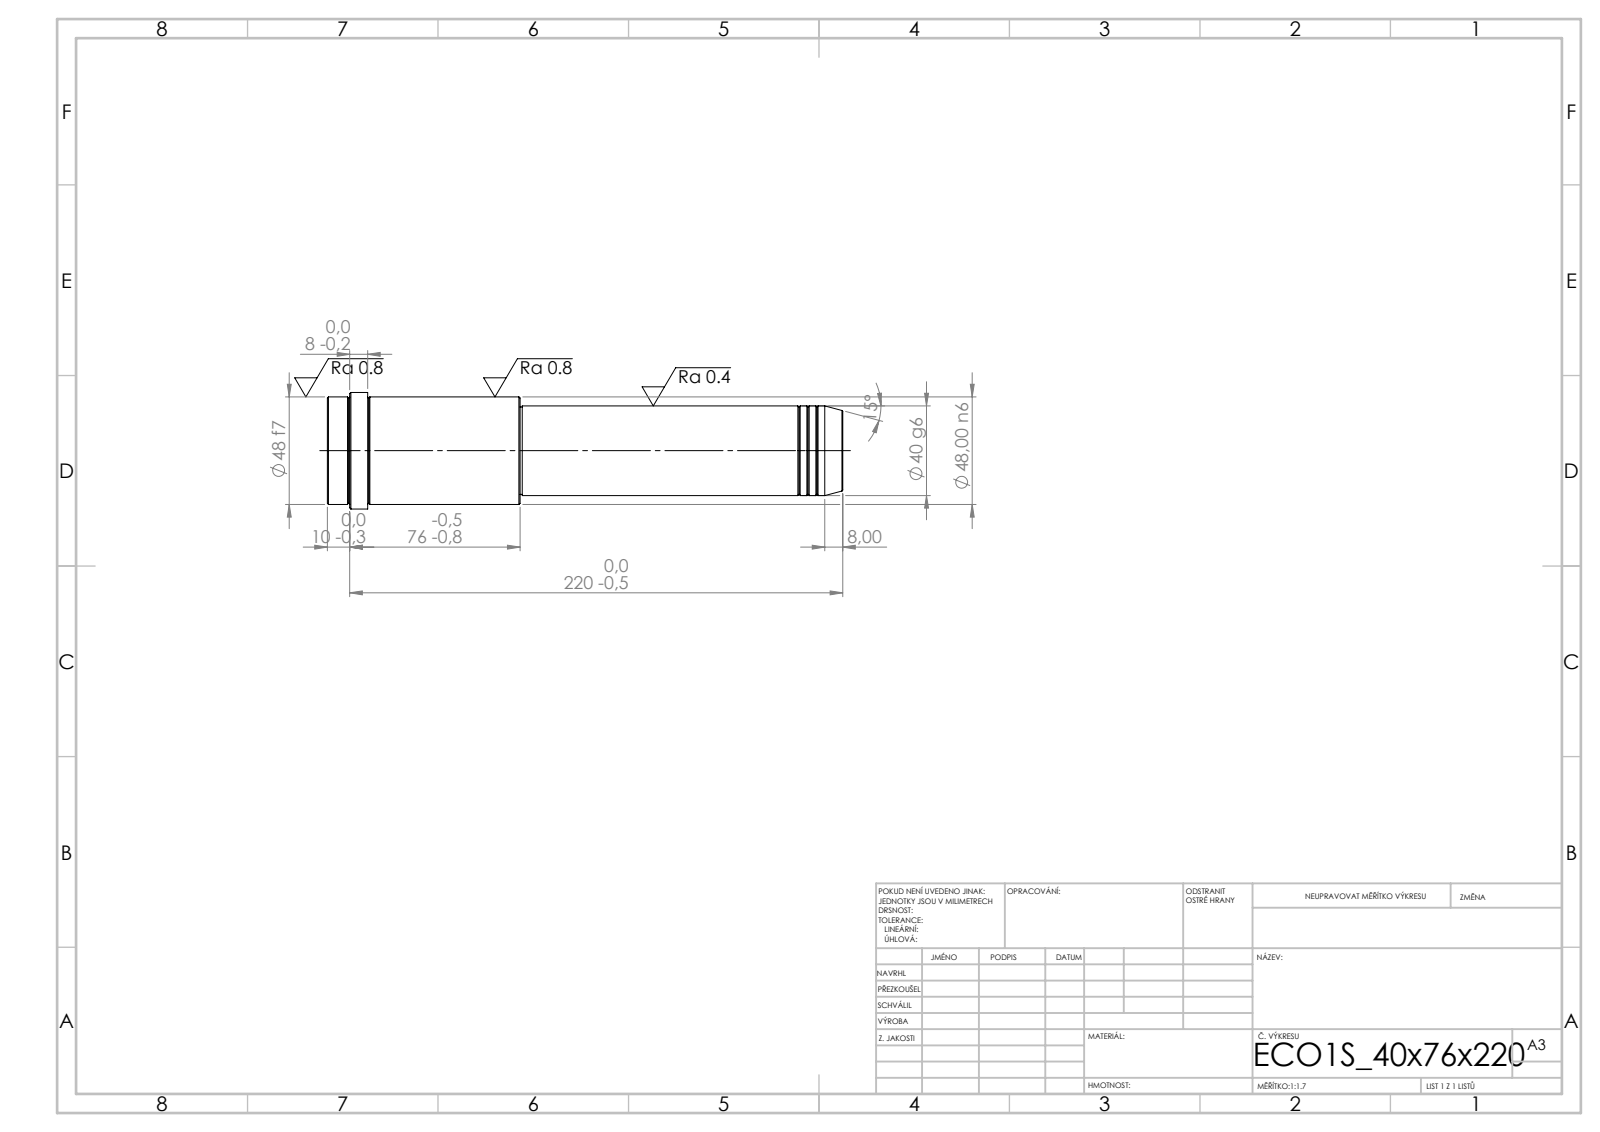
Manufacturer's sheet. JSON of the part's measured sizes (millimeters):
{"step_written_by": "SolidWorks 2019 (CONFIG_CONTROL_DESIGN)", "units": "millimeters", "bodies": {"solids": 1, "faces": 52, "planar": 6, "cylindrical": 16, "other": 30}, "overall_size": [230, 52, 52], "volume_mm3": 337665, "surface_area_mm2": 35479, "round_bosses_or_shafts": [[52, 1], [48, 1], [40, 1], [39, 1]], "face_to_face_distances": [230, 144, 86, 212, 68, 18, 220, 76, 8, 10]}
